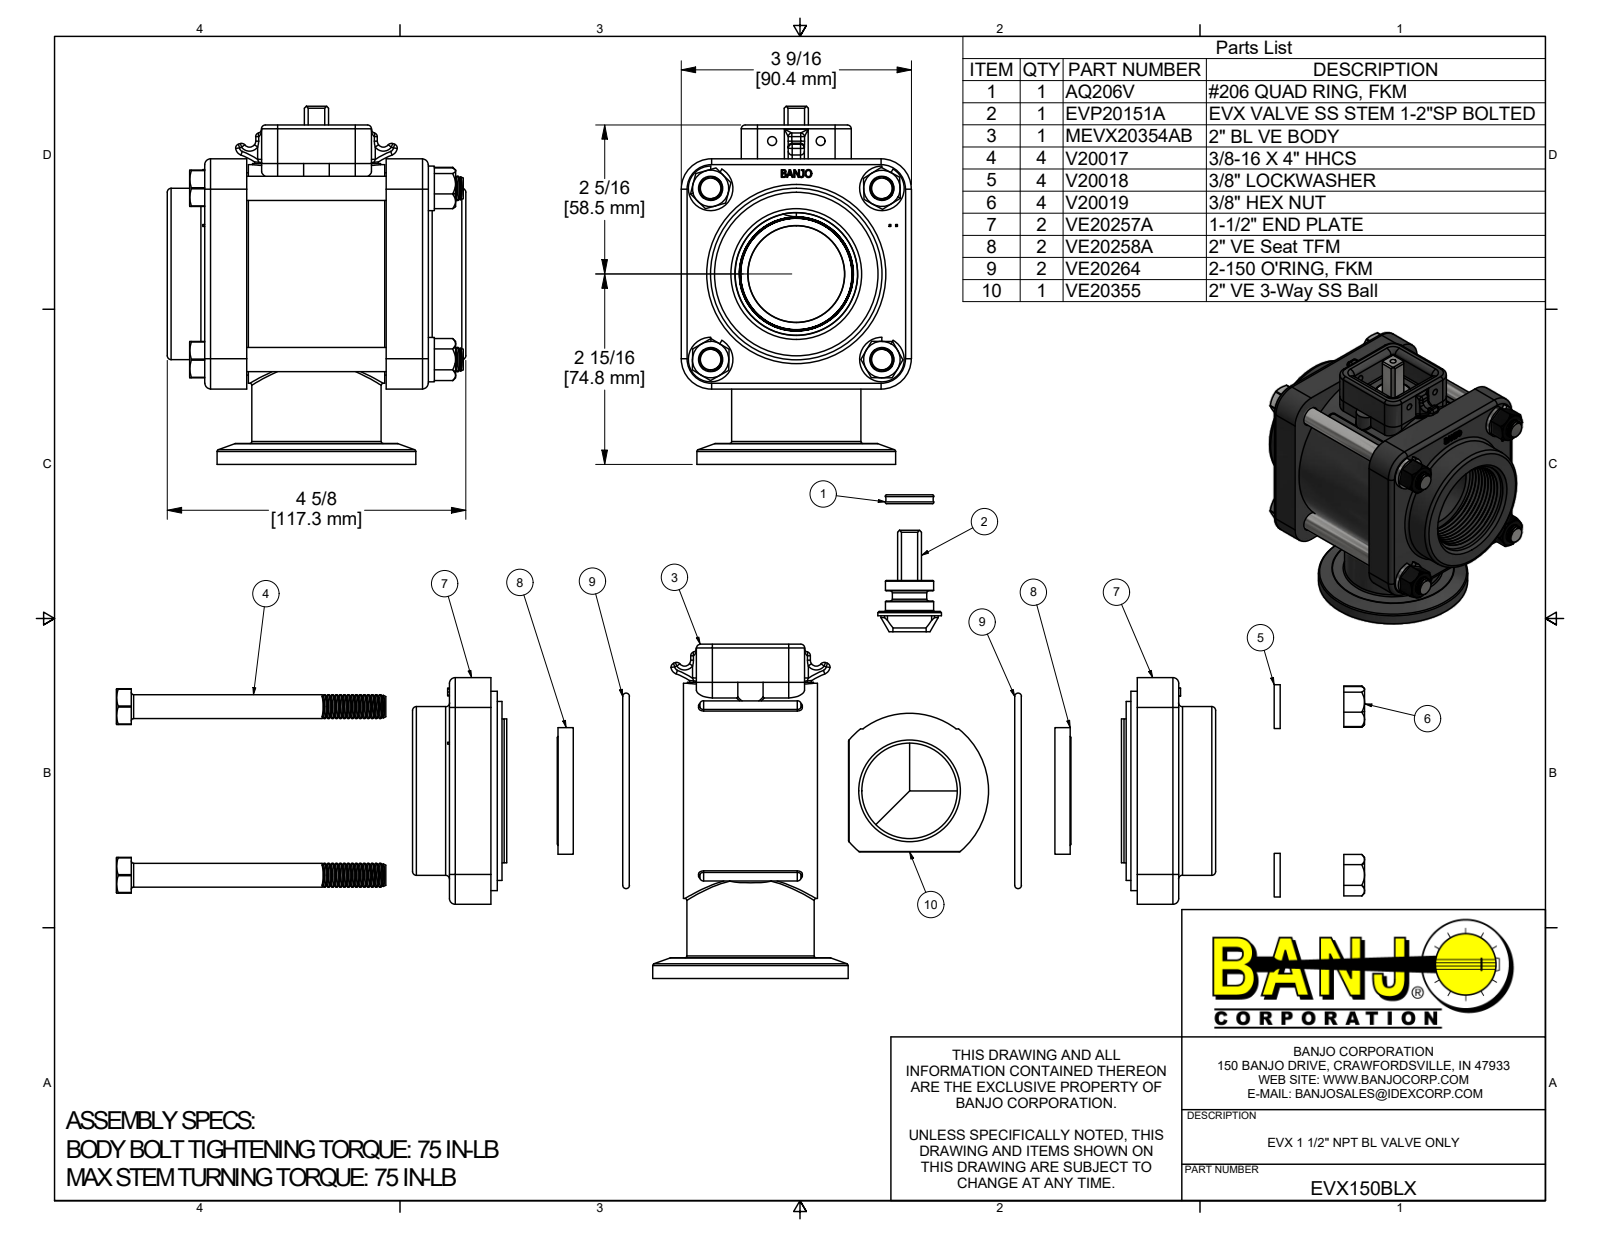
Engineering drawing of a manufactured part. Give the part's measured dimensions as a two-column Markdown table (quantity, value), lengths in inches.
| quantity | value |
| --- | --- |
| part name | EVX150BLX; MEVX20354AB; MEVX20354ABX; V20017 (+8 more) |
| STEP written by | Autodesk Inventor 2019 (AUTOMOTIVE_DESIGN) |
| units | inches |
| bodies | 22 solids, 1290 faces (342 planar, 387 cylindrical, 561 other) |
| overall size | 5.538 × 4.618 × 3.56 |
| volume | 34.19 in³ |
| surface area | 264.4 in² |
| round holes (diameter × count) | 0.307 × 4, 0.385 × 4, 0.406 × 4, 1.5 × 3, 0.135 × 2, 0.76 × 1, 1.02 × 1, 1.48 × 1, 1.495 × 1, 1.995 × 1, 2.185 × 1, 2.56 × 1 |
| round bosses / shafts (diameter × count) | 0.324 × 60, 0.687 × 4, 0.375 × 4, 3.38 × 1, 3.13 × 1, 3.074 × 1, 2.812 × 1, 2.65 × 1 |
| partial cylindrical surfaces (radius × count) | 0.06 × 28, 0.09 × 12, 0.02 × 8, 0.162 × 8, 0.125 × 6, 0.015 × 4, 0.03 × 4, 0.21 × 4 |
| main face-to-face distances | 0.65, 2.808, 0.825, 2.633, 0.175, 1.983, 3.56, 0.1, 1.883, 3.458 |
| hole center spacings | 1.872, 2.648, 1.198, 1.849, 2.088, 3.509, 3.745, 3.781 |
